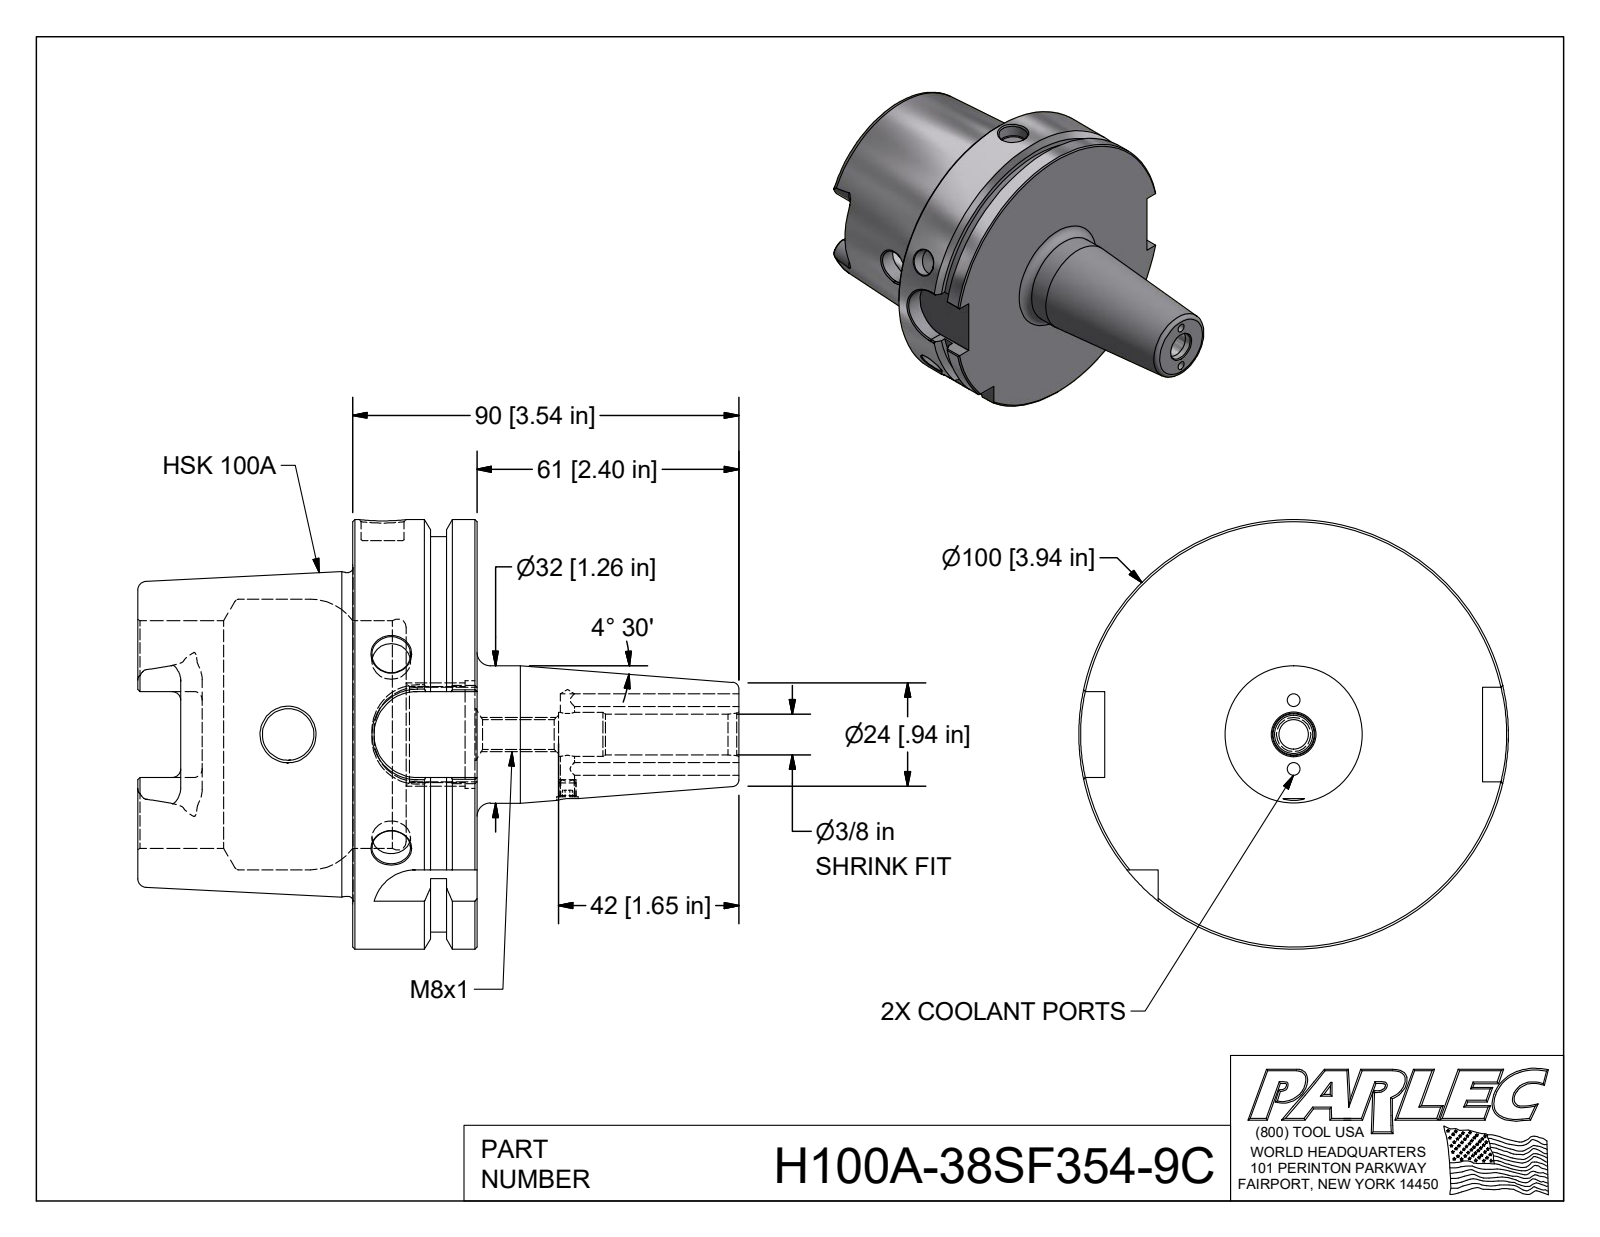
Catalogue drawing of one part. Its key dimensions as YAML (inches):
step_written_by: "Autodesk Inventor 2018 (AUTOMOTIVE_DESIGN)"
units: inches
bodies: {solids: 1, faces: 150, planar: 49, cylindrical: 42, other: 59}
overall_size: [5.509, 3.937, 3.937]
volume: 17.64
surface_area: 89.08
round_holes:
  - {diameter: 0.118, count: 2}
  - {diameter: 0.354, count: 2}
  - {diameter: 0.472, count: 2}
  - {diameter: 0.128, count: 1}
  - {diameter: 0.197, count: 1}
  - {diameter: 0.272, count: 1}
  - {diameter: 0.374, count: 1}
  - {diameter: 0.394, count: 1}
  - {diameter: 0.404, count: 1}
  - {diameter: 0.881, count: 1}
  - {diameter: 0.985, count: 1}
  - {diameter: 2.087, count: 1}
round_bosses_or_shafts:
  - {diameter: 3.937, count: 1}
  - {diameter: 3.622, count: 1}
  - {diameter: 2.967, count: 1}
  - {diameter: 1.26, count: 1}
partial_cylinders:
  - {radius: 0.079, count: 6}
  - {radius: 0.192, count: 4}
  - {radius: 0.394, count: 4}
face_to_face_distances: [1.142, 0.492, 0.65, 1.969, 2.461, 3.11, 3.465, 2.83, 0.861, 0.369]
hole_center_spacings: [0.315, 0.63, 1.694]
